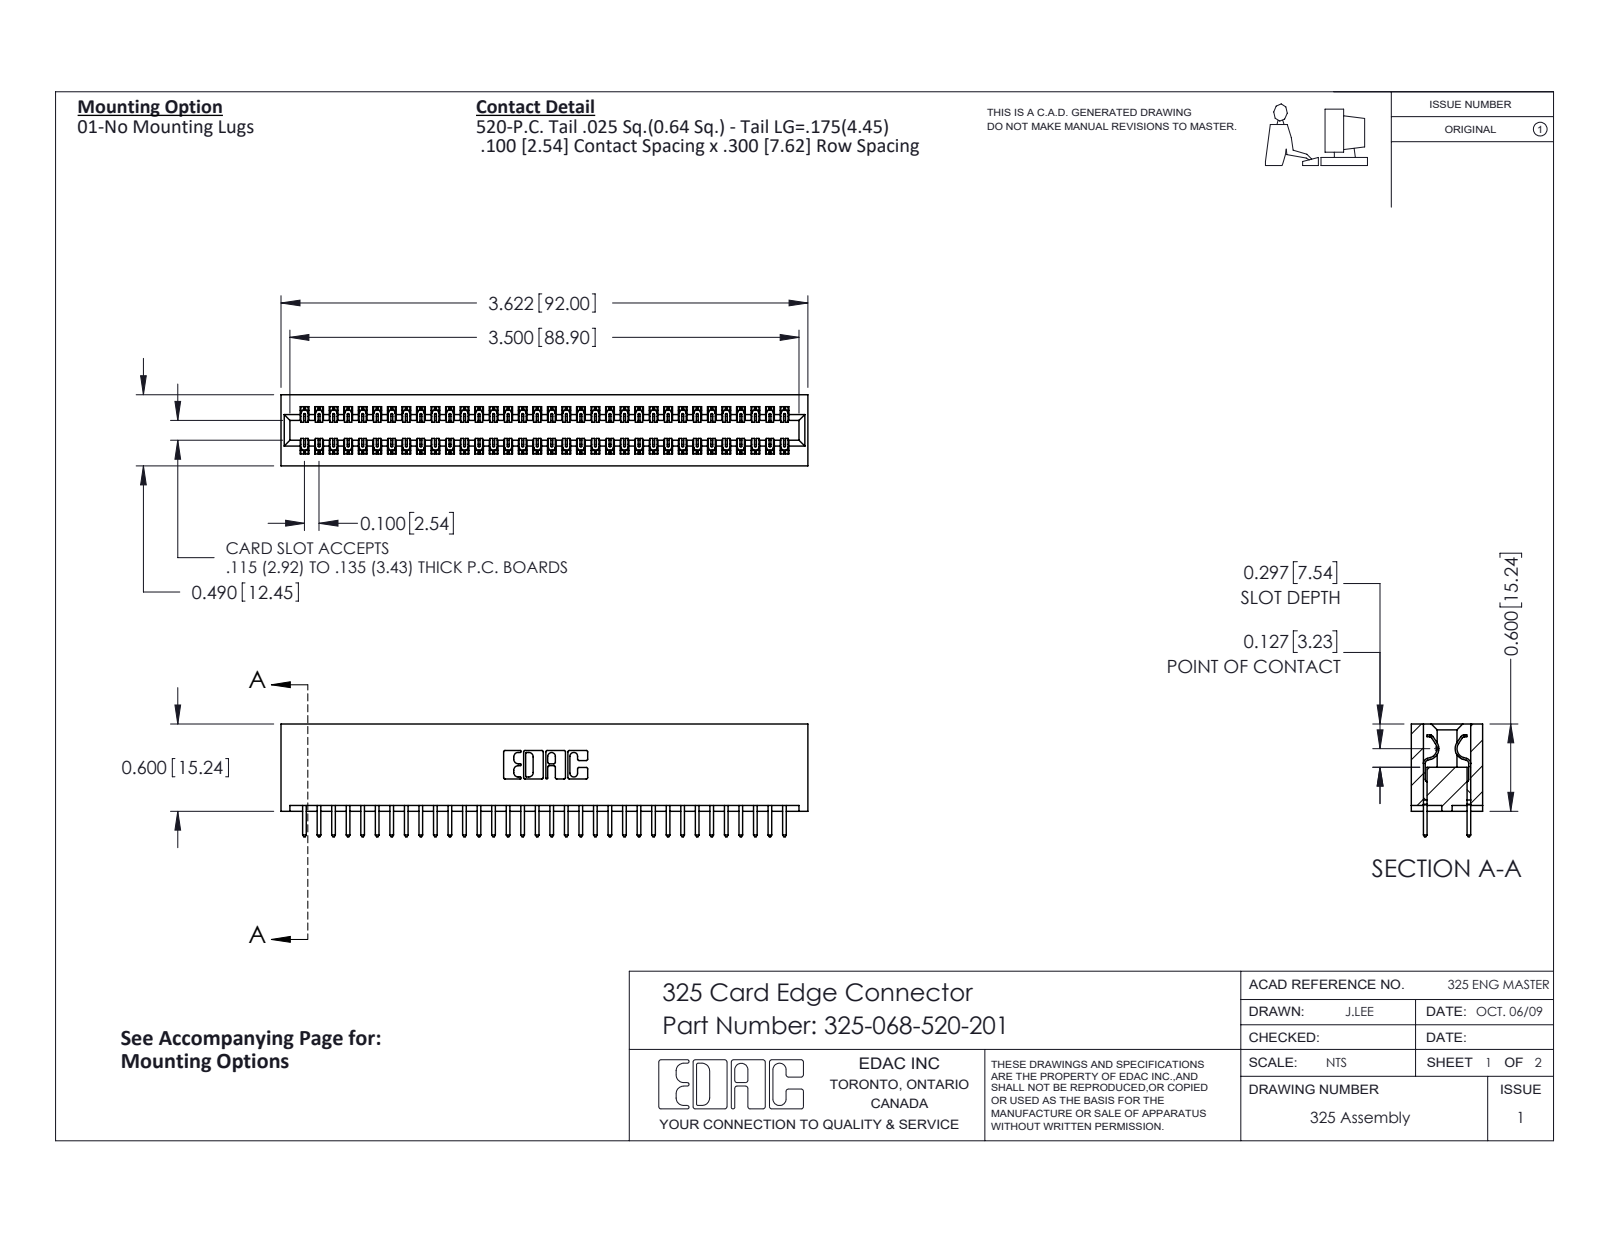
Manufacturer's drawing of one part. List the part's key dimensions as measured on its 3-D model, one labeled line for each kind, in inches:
Part name (STEP PRODUCT): 325-292-001_325-293-120; 325-068-520-201; 325 Part_Lugless
STEP written by: SolidWorks 2016 (CONFIG_CONTROL_DESIGN)
Units: inches
Bodies: 69 solids, 3642 faces (2514 planar, 1128 cylindrical, 0 other)
Overall size (bounding box): 3.622 × 0.775 × 0.49
Volume: 0.757 in³ · Surface area: 23.78 in²
Partial cylindrical surfaces — rounded edges, fillets, slot ends (radius × count): R0.006 ×102, R0.01 ×68, R0.01 ×22, R0.007 ×6, R0.031 ×6, R0.026 ×3, R0.014 ×2, R0.022 ×2
Main face-to-face distances: 0.083, 0.407, 0.3, 0.49, 0.107, 0.383, 0.025, 0.325, 0.275, 0.1
